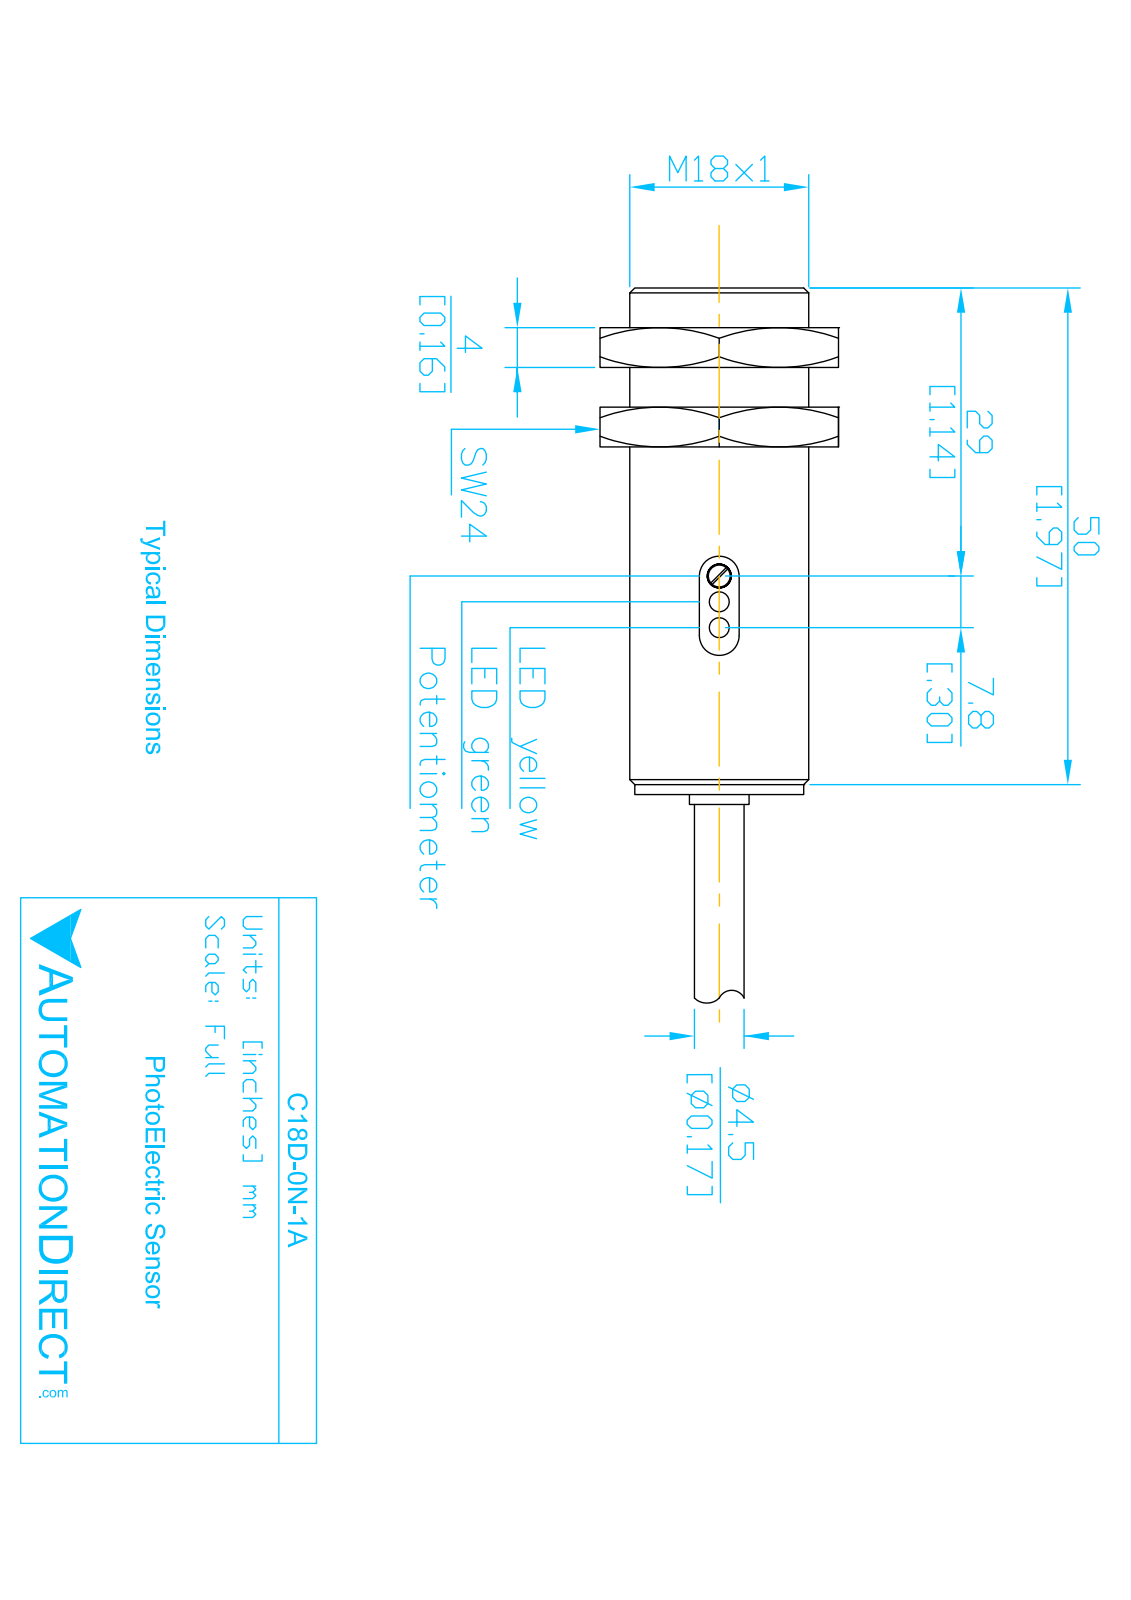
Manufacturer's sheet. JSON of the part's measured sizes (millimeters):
{"part_name": "C18D-0N-1A", "step_written_by": "SolidWorks 2017 (AUTOMOTIVE_DESIGN)", "units": "millimeters", "bodies": {"solids": 1, "faces": 26, "planar": 10, "cylindrical": 5, "other": 11}, "overall_size": [78.4, 18, 18], "volume_mm3": 13300, "surface_area_mm2": 3729, "round_bosses_or_shafts": [[18, 1], [16.4, 1], [10.5, 1], [6.8, 1], [4.3, 1]], "face_to_face_distances": [50.8, 51.6, 0.8, 51, 51.8, 53, 52.8, 2, 1.2]}
